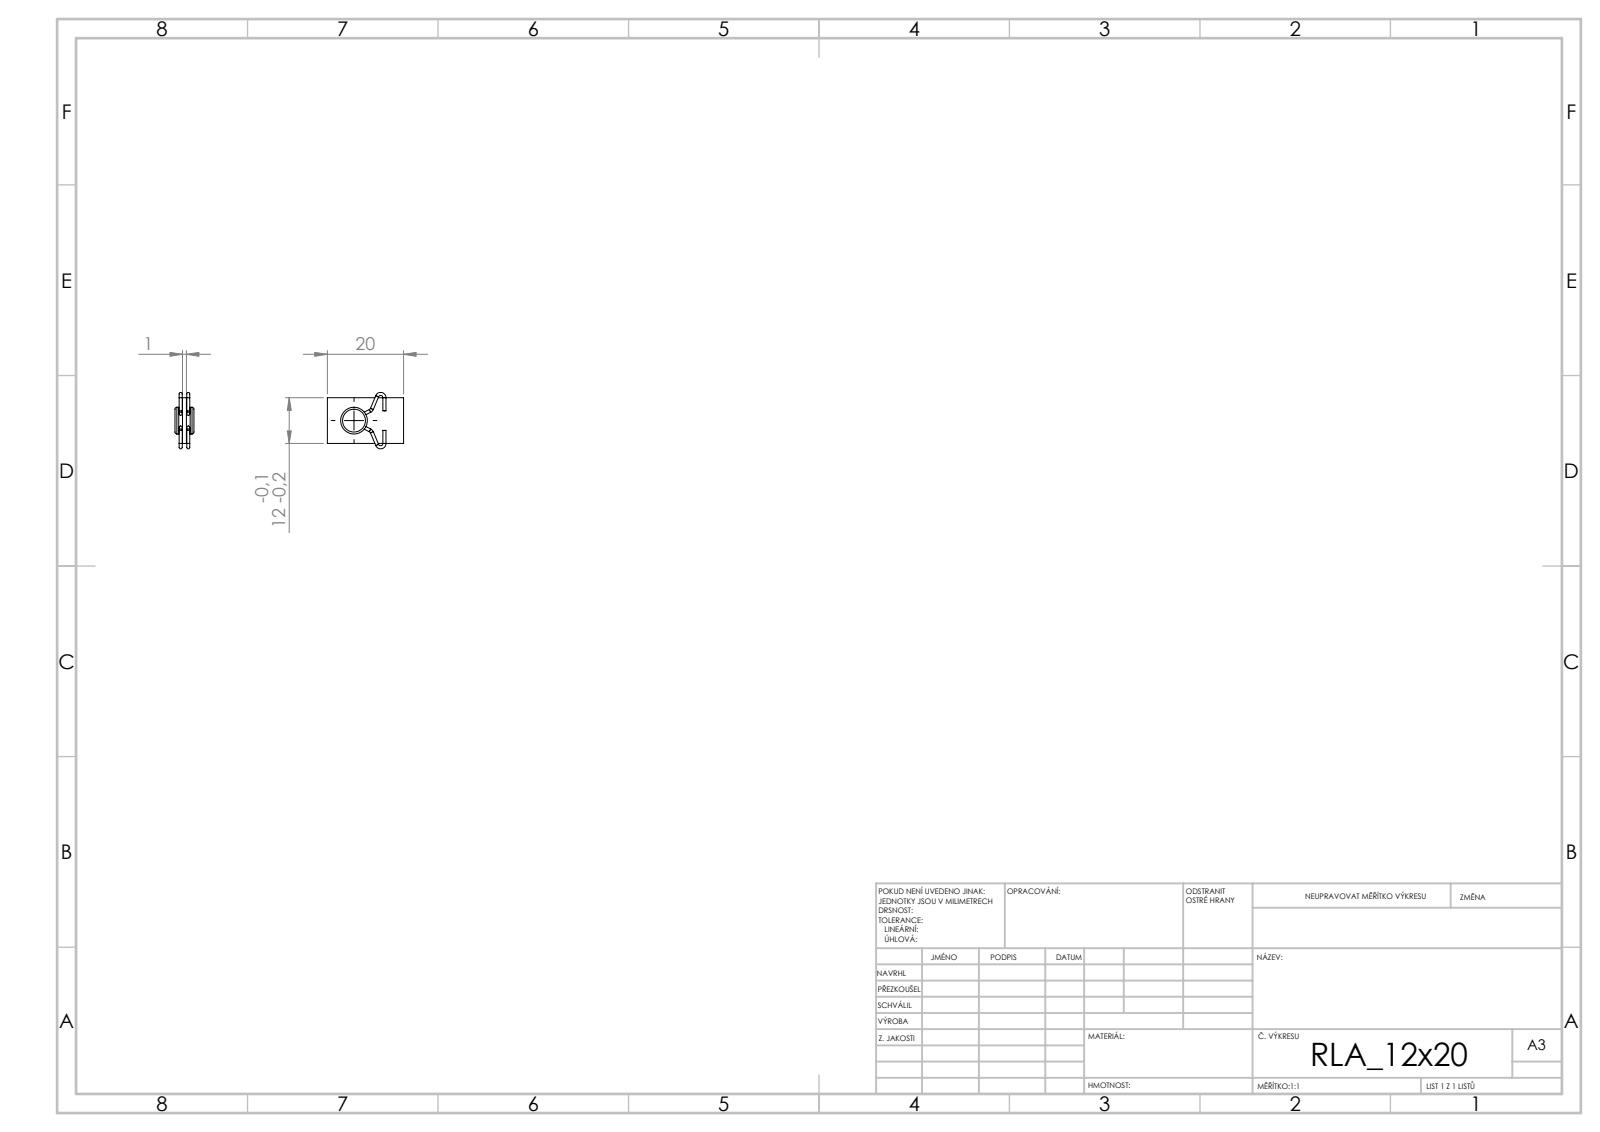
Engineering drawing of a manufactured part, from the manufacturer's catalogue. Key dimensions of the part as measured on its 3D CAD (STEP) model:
STEP written by: SolidWorks 2019 (CONFIG_CONTROL_DESIGN)
Units: millimetres
Bodies: 3 solids, 82 faces (14 planar, 40 cylindrical, 28 other)
Overall size (bounding box): 20 × 14.8 × 5
Volume: 378 mm³ · Surface area: 900 mm²
Round bosses / shafts (diameter × count): ⌀0.8 ×14, ⌀7 ×1, ⌀4 ×1
Main face-to-face distances: 1, 2, 3, 4, 5, 12, 20, 3.45, 8.55, 5.1
